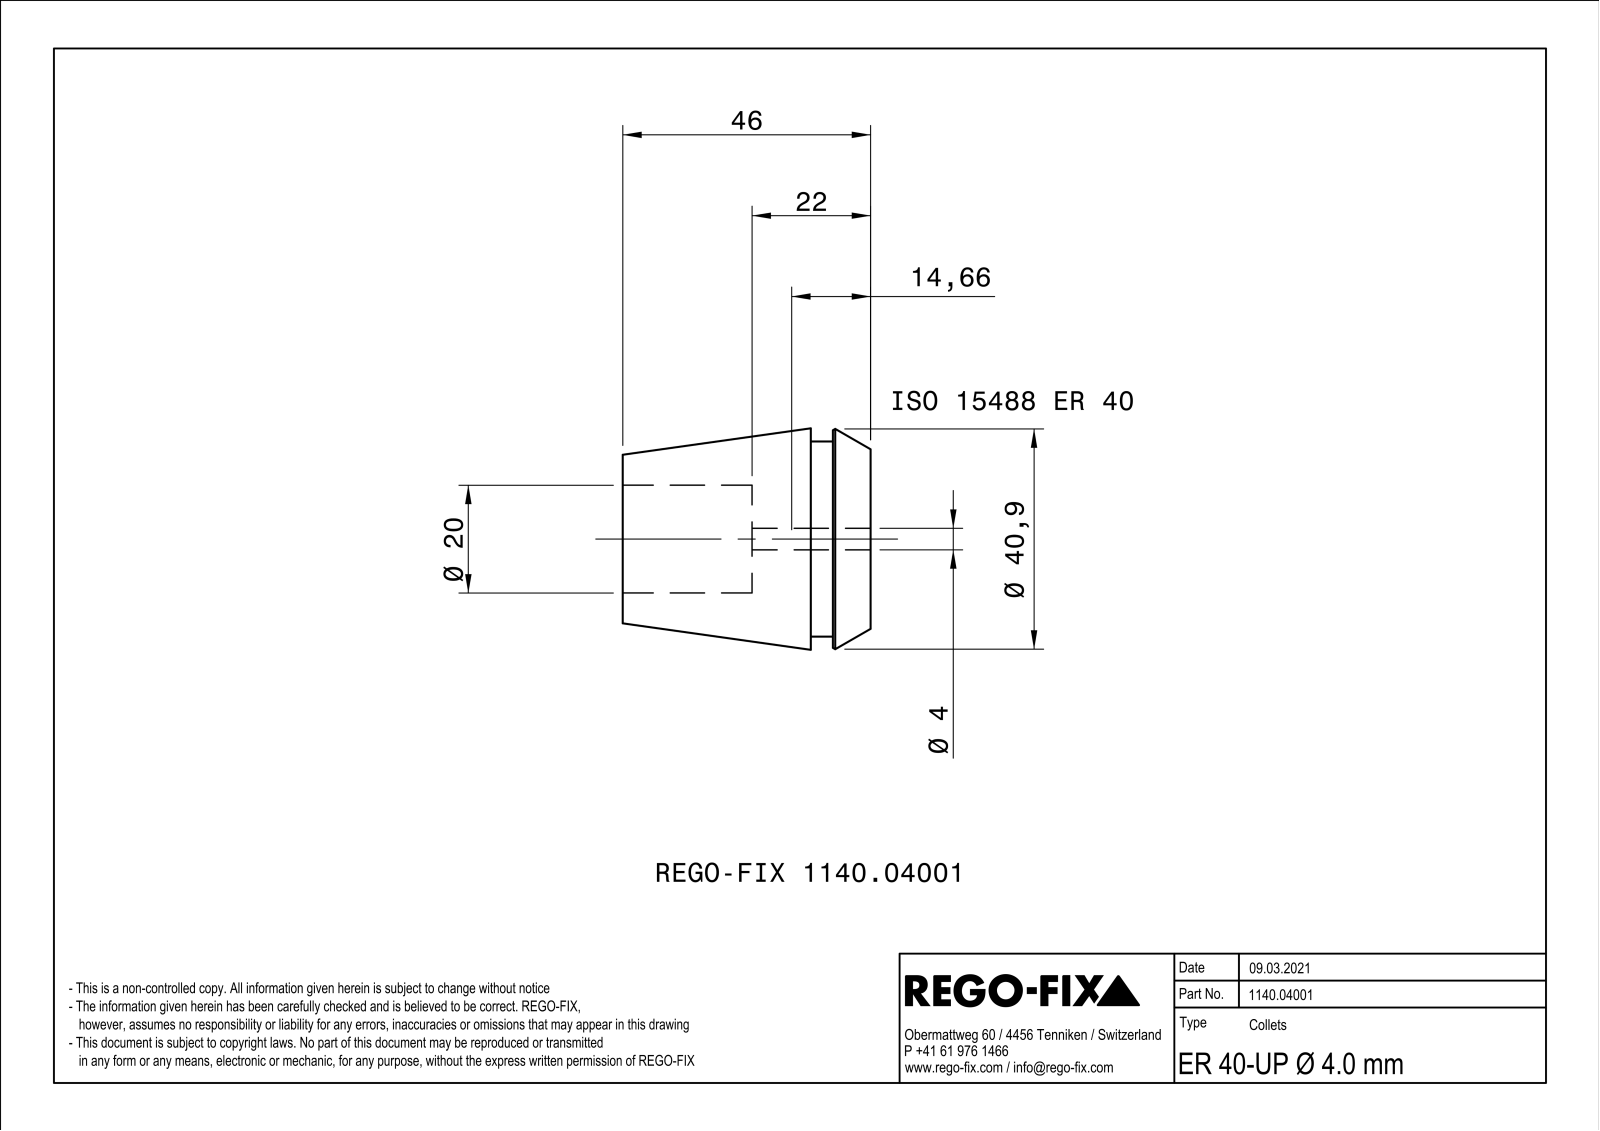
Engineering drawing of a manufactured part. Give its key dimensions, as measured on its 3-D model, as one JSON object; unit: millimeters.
{"part_name": "NOCUT", "step_written_by": "SIEMENS PLM Software Solid Edge ST10 (AUTOMOTIVE_DESIGN)", "units": "millimeters", "bodies": {"solids": 1, "faces": 272, "planar": 104, "cylindrical": 48, "other": 120}, "overall_size": [46, 41.09, 41.09], "volume_mm3": 34965, "surface_area_mm2": 21298, "round_holes": [[20, 1]], "round_bosses_or_shafts": [[36.2, 1]], "partial_cylinders_radius": [[45, 8], [2, 1]], "face_to_face_distances": [0.8, 0.78, 0.82, 46, 11.1, 34.9, 7, 4.1, 39, 22]}
